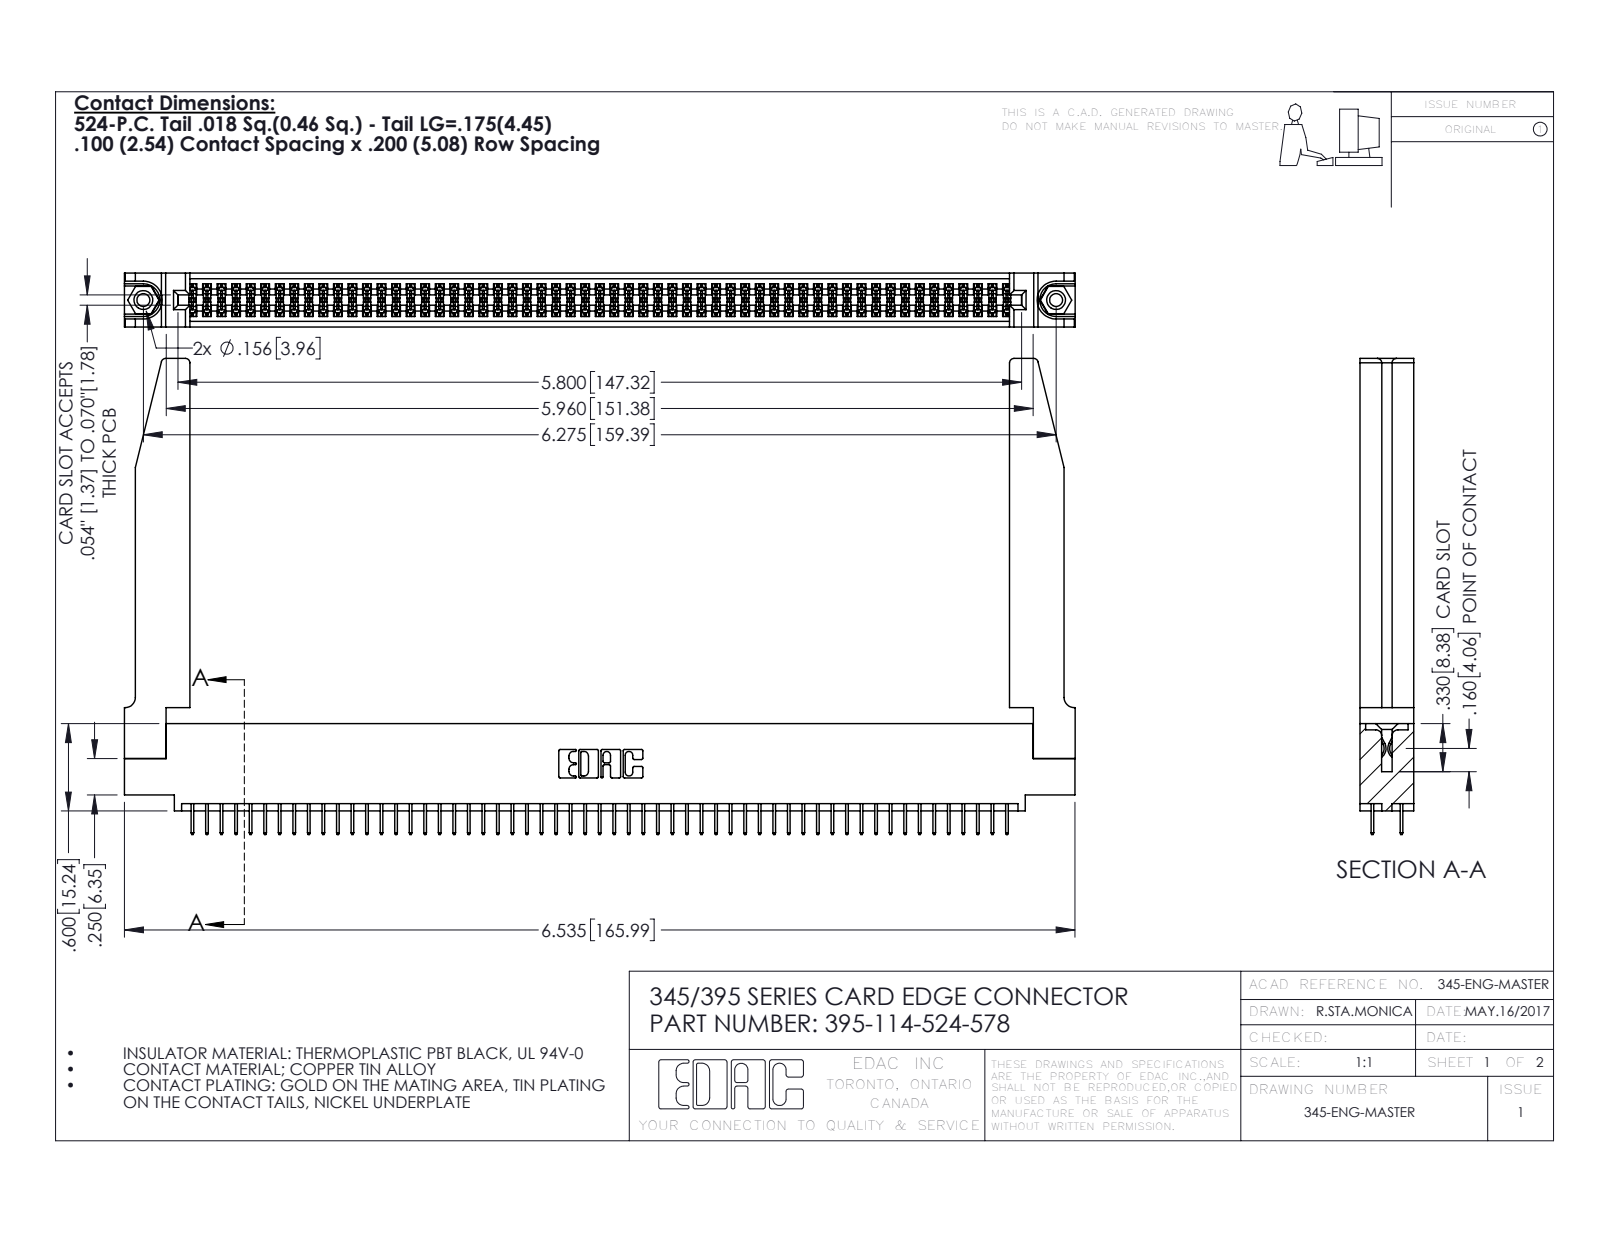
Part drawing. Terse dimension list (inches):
name: 345 Part_0.110 Offset - 0.156 Dia-TH; 345-292-001_345-293-124; 345-250-001_345-250-001-102; 395-114-524-578 (+1 more)
written by: SolidWorks 2016 (CONFIG_CONTROL_DESIGN)
unit: in
bodies: 119 solids, 6520 faces (4672 planar, 1796 cylindrical, 52 other)
size: 6.536 × 3.272 × 0.37
volume: 1.452 in³; area: 47.19 in²
holes: 2× ⌀0.089, 2× ⌀0.125, 2× ⌀0.156, 1× ⌀0.064
bosses: 2× ⌀0.155
rounds: 171× R0.006, 22× R0.01, 8× R0.03, 6× R0.007, 6× R0.031, 3× R0.026, 2× R0.014, 2× R0.019
face distances: 0.072, 0.37, 0.298, 0.2, 0.098, 0.272, 0.025, 0.225, 0.072, 0.175
hole spacings: 0.27, 6.039, 6.275
